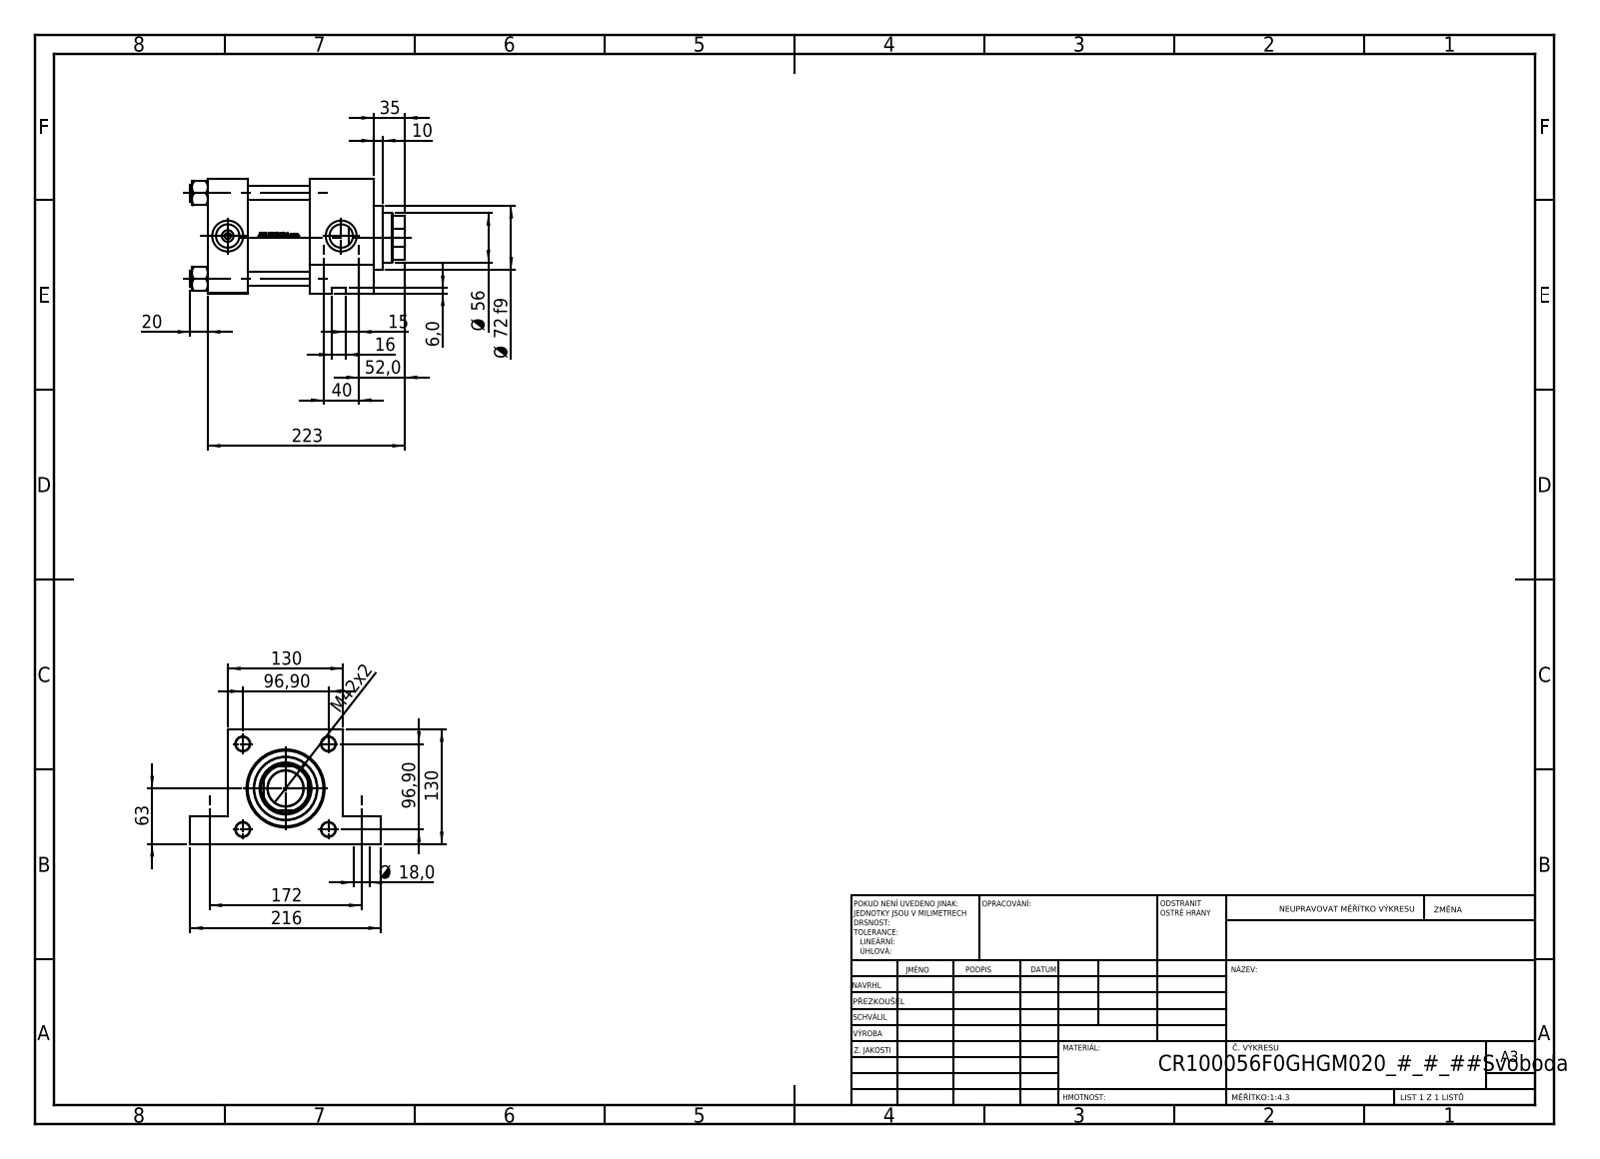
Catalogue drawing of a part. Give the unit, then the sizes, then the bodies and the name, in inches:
Units: inches
Overall size (bounding box): 9.567 × 8.504 × 5.118
Round holes (diameter × count): ⌀0.63 ×4, ⌀0.709 ×4, ⌀0.276 ×2, ⌀1.041 ×2, ⌀1.378 ×2, ⌀1.594 ×1, ⌀2.205 ×1, ⌀2.323 ×1, ⌀2.992 ×1, ⌀3.366 ×1, ⌀3.937 ×1
Round bosses / shafts (diameter × count): ⌀0.748 ×4, ⌀4.173 ×1, ⌀2.835 ×1
Partial cylindrical surfaces — rounded edges, fillets, slot ends (radius × count): R1.063 ×1
Main face-to-face distances: 5.118, 1.772, 7.402, 5.63, 4.567, 2.795, 2.835, 0.787, 1.26, 3.622
Hole centre spacings: 3.815, 1.575, 2.643, 2.754, 5.395, 6.772, 6.952, 5.059
Volume: 160.8 in³ · Surface area: 550.1 in²
Bodies: 11 solids, 1151 faces (485 planar, 126 cylindrical, 540 other)
Part name (STEP PRODUCT): V215CR_F_Body; NUT_M5_F; V215CR_F_TYCINKA; V215CR_VCP_F (+1 more)
STEP written by: SolidWorks 2019 (CONFIG_CONTROL_DESIGN)
